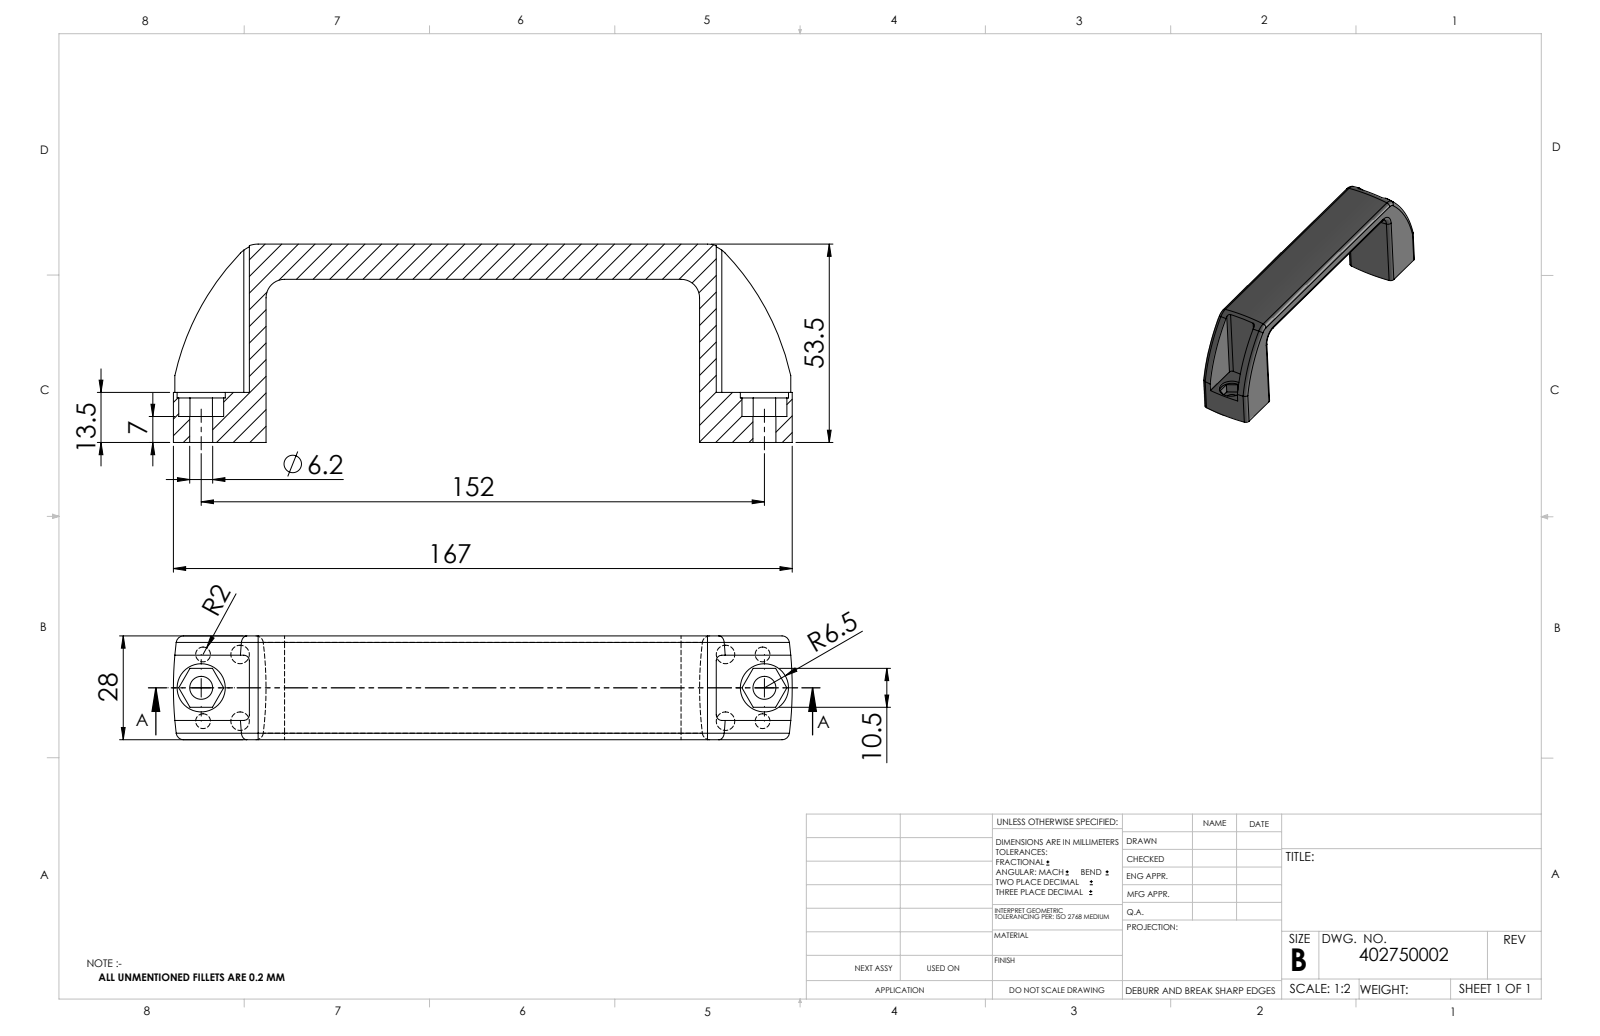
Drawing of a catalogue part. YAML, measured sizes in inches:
part_name: "402750002_c_1"
step_written_by: "SolidWorks 2014 (CONFIG_CONTROL_DESIGN)"
units: inches
bodies: {solids: 1, faces: 102, planar: 36, cylindrical: 46, other: 20}
overall_size: [6.575, 2.106, 1.102]
volume: 3.91
surface_area: 36.36
round_holes:
  - {diameter: 0.157, count: 4}
  - {diameter: 0.197, count: 4}
  - {diameter: 0.244, count: 2}
  - {diameter: 0.512, count: 2}
partial_cylinders:
  - {radius: 0.079, count: 12}
  - {radius: 3.937, count: 6}
  - {radius: 0.059, count: 4}
face_to_face_distances: [1.102, 0.205, 0.898, 0.693, 4.961, 0.531, 0.413, 0.276, 0.256, 0.039]
hole_center_spacings: [0.355, 0.394, 0.544, 0.709, 0.811, 5.551, 5.582, 5.596]
